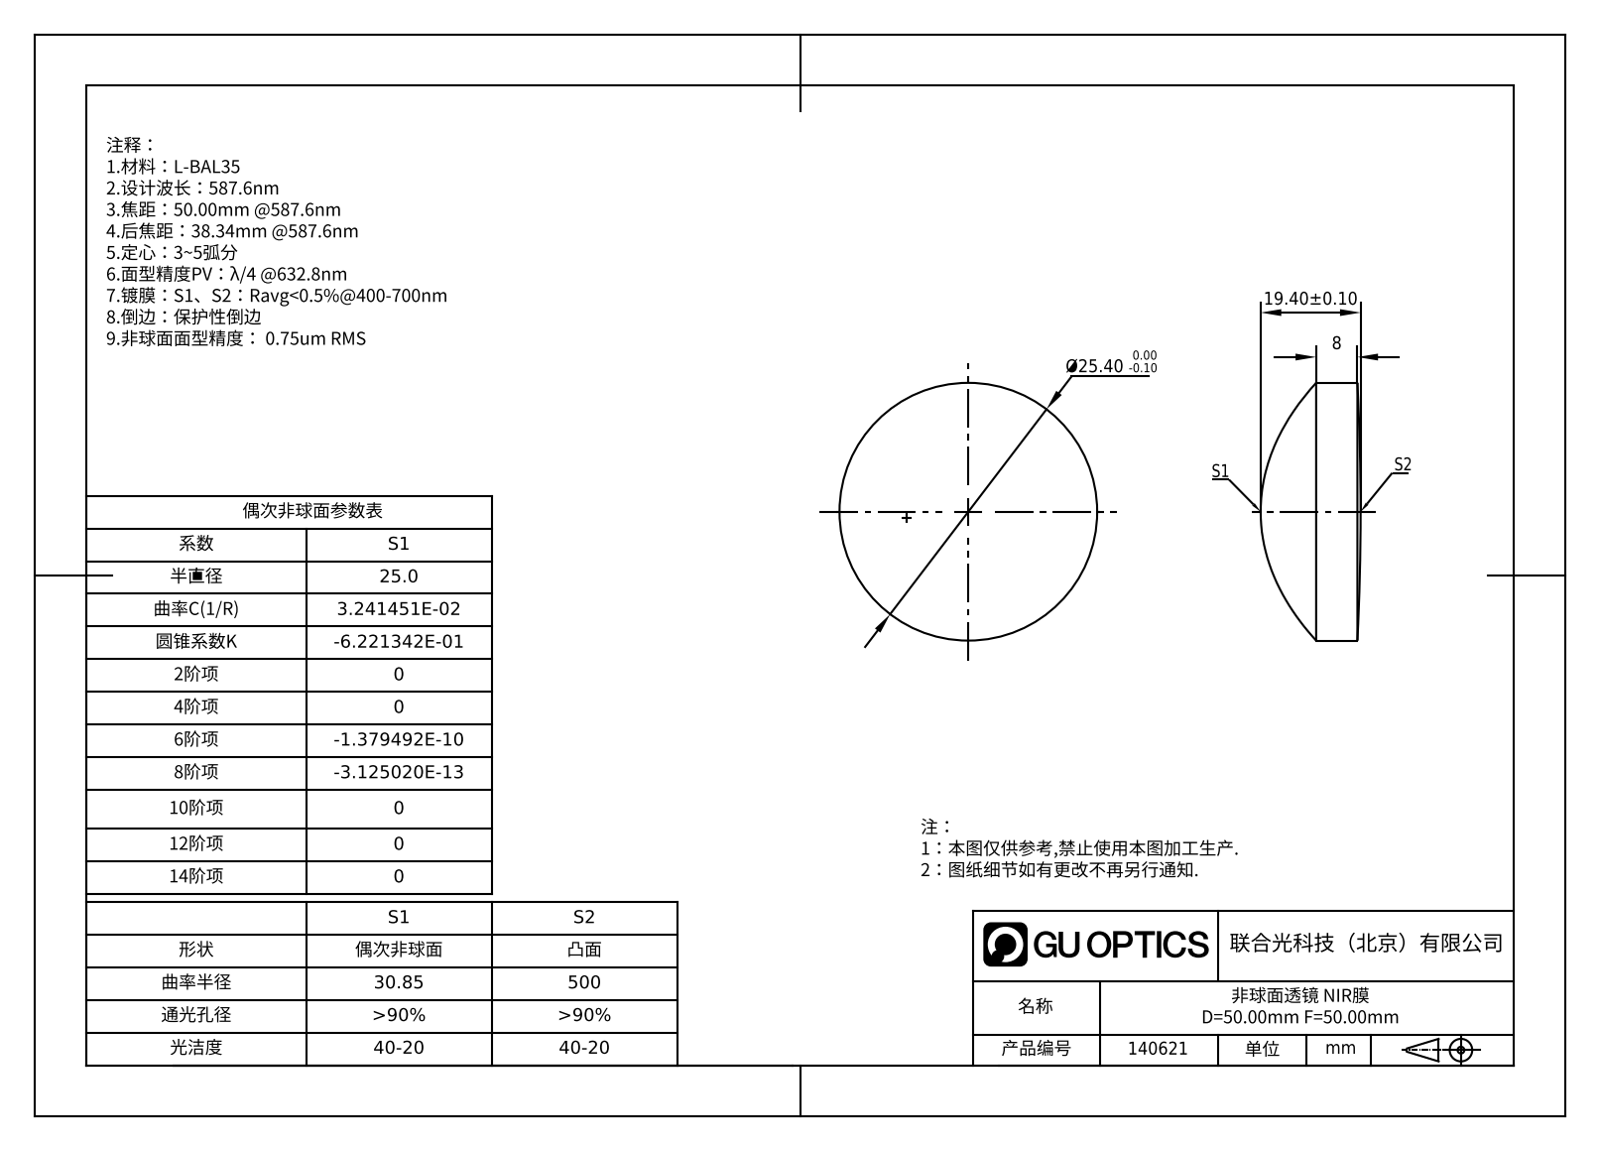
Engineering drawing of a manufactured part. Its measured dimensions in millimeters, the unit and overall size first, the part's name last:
Units: millimetres
Overall size (bounding box): 50 × 50 × 19.4
Round bosses / shafts (diameter × count): ⌀50 ×1
Volume: 27 118 mm³ · Surface area: 5 525 mm²
Bodies: 1 solid, 5 faces (0 planar, 2 cylindrical, 3 other)
Part name (STEP PRODUCT): 140611
STEP written by: SolidWorks 2020 (CONFIG_CONTROL_DESIGN)
